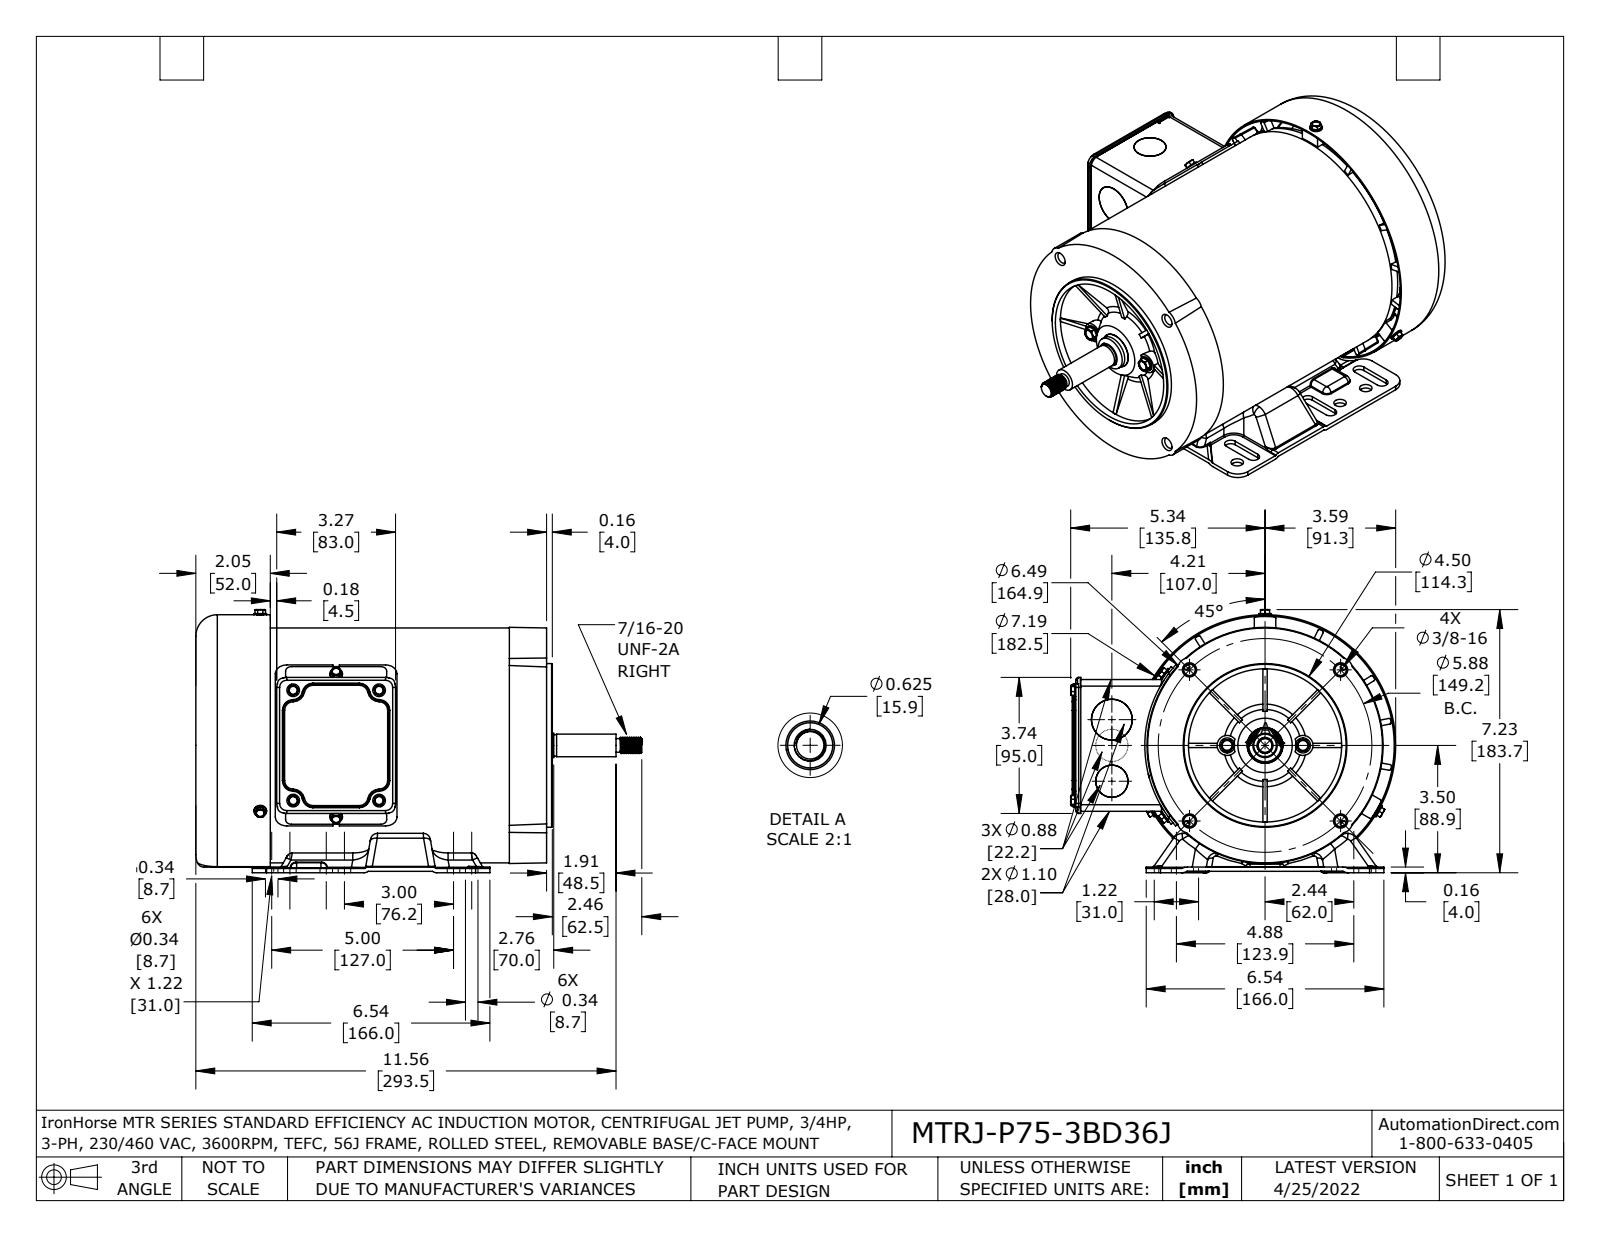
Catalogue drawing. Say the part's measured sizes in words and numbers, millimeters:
The part is named "MTRJ-P75-3BD36J redcmb1 coord fxt". Its 3-D file was written by "SolidWorks 2021 (AUTOMOTIVE_DESIGN)". It is 29 solids with 2729 faces: 658 planar, 899 cylindrical and 1172 other. Overall it measures 311.5 by 227 by 183.7 millimeters. Its volume is 757 900 cubic millimeters and its surface area 576 000 square millimeters. Round holes: 10 of diameter 5, 9 of diameter 5.6, 8 of diameter 7, 7 of diameter 3.5, 6 of diameter 5.5, 6 of diameter 8.3, 6 of diameter 8.7, 4 of diameter 3.8, 4 of diameter 4.5, 4 of diameter 8, 2 of diameter 3.4, 2 of diameter 6.9. Round bosses or shafts: 9 of diameter 4.2, 8 of diameter 8.8, 6 of diameter 6, 2 of diameter 10.5, 2 of diameter 4.8, 1 of diameter 182.5, 1 of diameter 114.3, 1 of diameter 24. Partial cylindrical surfaces (rounded edges, fillets, slot ends): 109 of radius 3, 65 of radius 1, 32 of radius 4, 30 of radius 0.5, 26 of radius 3.5, 18 of radius 2, 18 of radius 7, 12 of radius 4.4. The main face-to-face distances are 1, 3, 1.6, 4, 245, 244, 2, 90.4, 78.4, 1.2. The hole center spacings are 107.2, 77, 2.4, 58.9, 61.2, 74.6, 75.7, 95.2.
